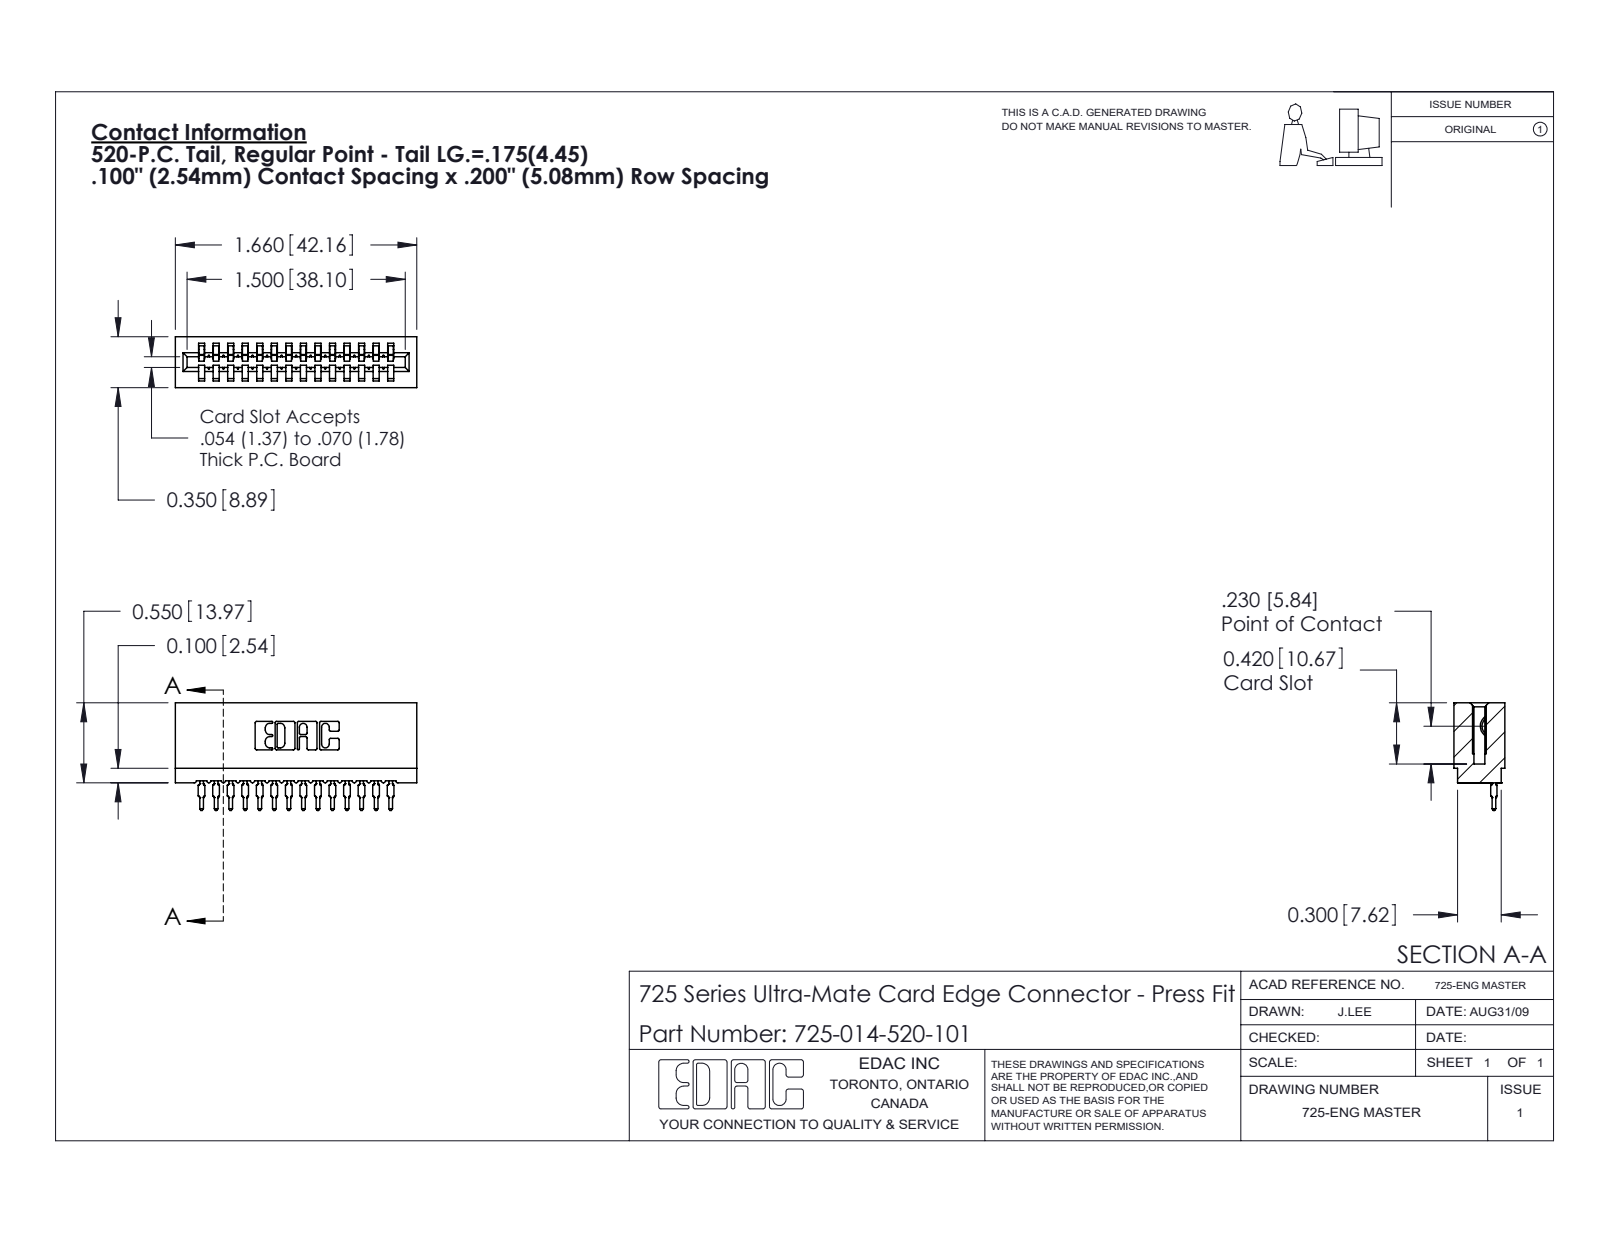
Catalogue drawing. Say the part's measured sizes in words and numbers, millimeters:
The part is named "725-014-520-101; 745-292-001_520; 725 Part_Insulator Option - 01". Its 3-D file was written by "SolidWorks 2020 (CONFIG_CONTROL_DESIGN)". It is 15 solids with 1663 faces: 993 planar, 306 cylindrical and 364 other. Overall it measures 42.2 by 18.8 by 8.9 millimeters. Its volume is 3 340 cubic millimeters and its surface area 5 834 square millimeters. Partial cylindrical surfaces (rounded edges, fillets, slot ends): 28 of radius 0.4, 28 of radius 0.5, 22 of radius 0.3, 6 of radius 0.2, 6 of radius 0.8, 4 of radius 0.1, 4 of radius 0.3, 3 of radius 0.7. The main face-to-face distances are 2.5, 5.1, 7.6, 10.2, 12.7, 8.9, 15.2, 5.4, 3.5, 17.8.
